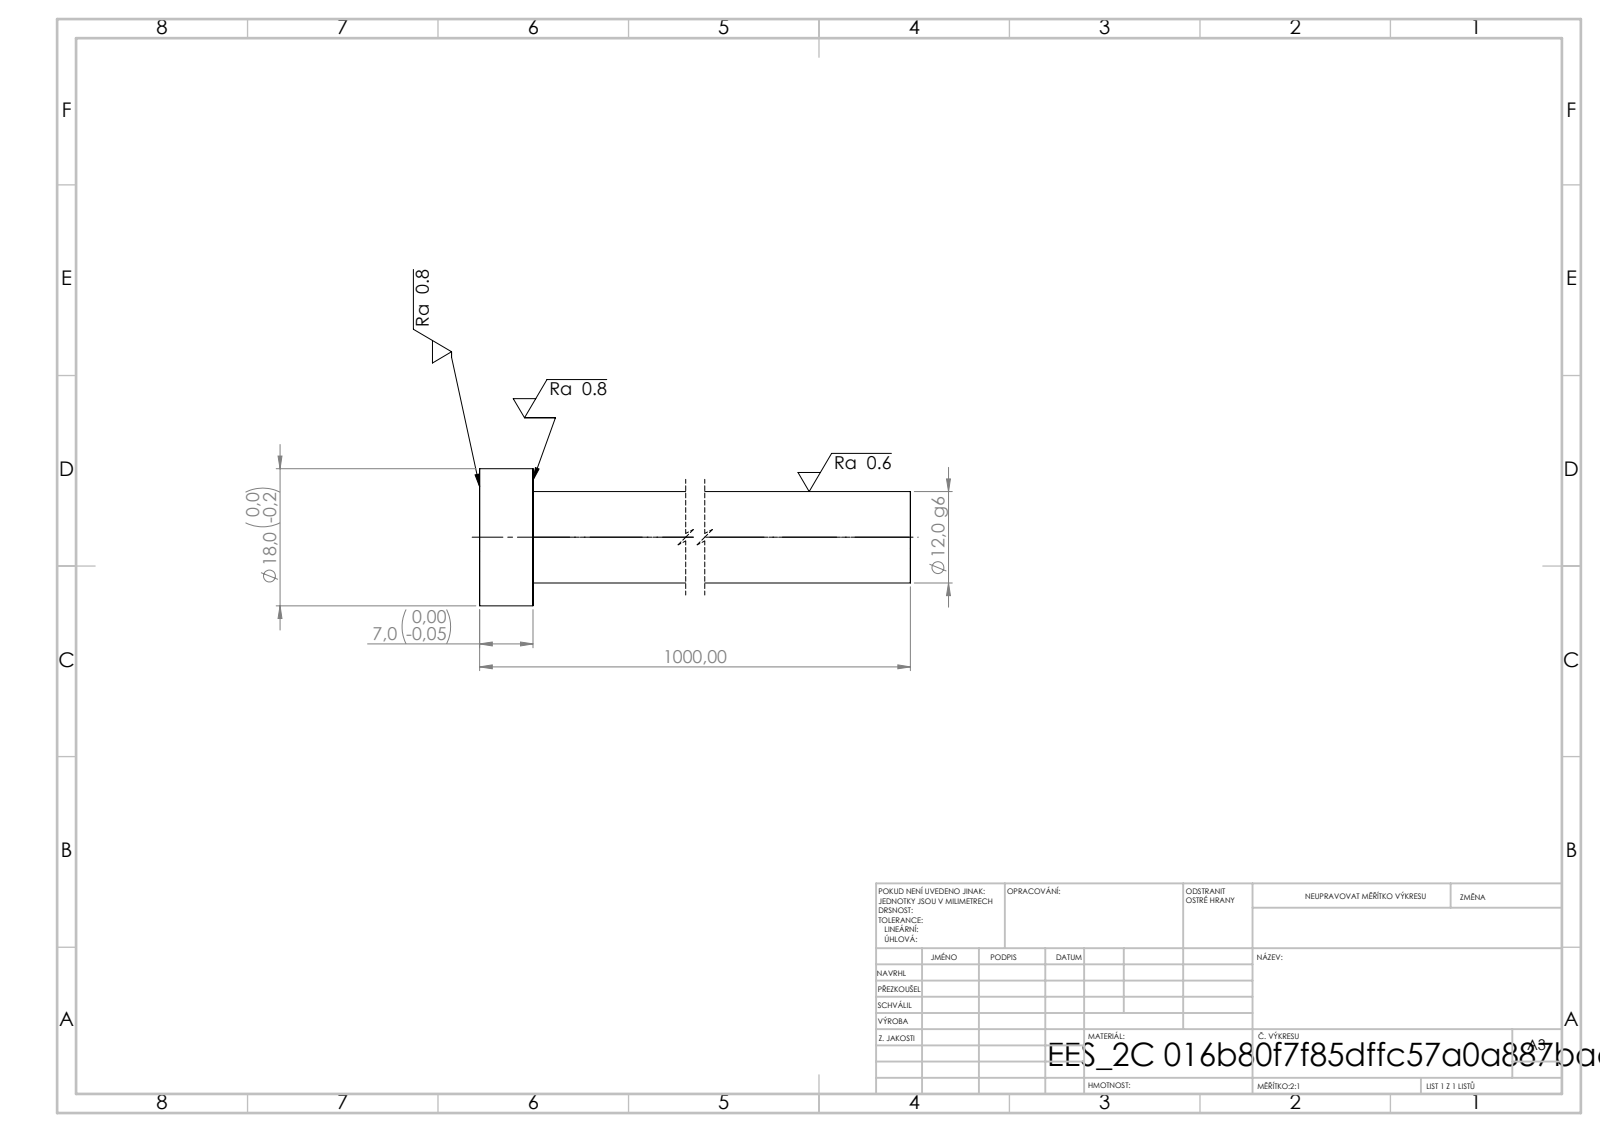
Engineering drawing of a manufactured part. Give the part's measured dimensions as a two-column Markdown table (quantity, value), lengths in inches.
| quantity | value |
| --- | --- |
| STEP written by | SolidWorks 2019 (CONFIG_CONTROL_DESIGN) |
| units | inches |
| bodies | 1 solid, 7 faces (3 planar, 4 cylindrical, 0 other) |
| overall size | 39.37 × 0.709 × 0.709 |
| volume | 6.962 in³ |
| surface area | 59.43 in² |
| round bosses / shafts (diameter × count) | 0.709 × 1, 0.472 × 1 |
| main face-to-face distances | 0.276, 39.37, 39.094 |
